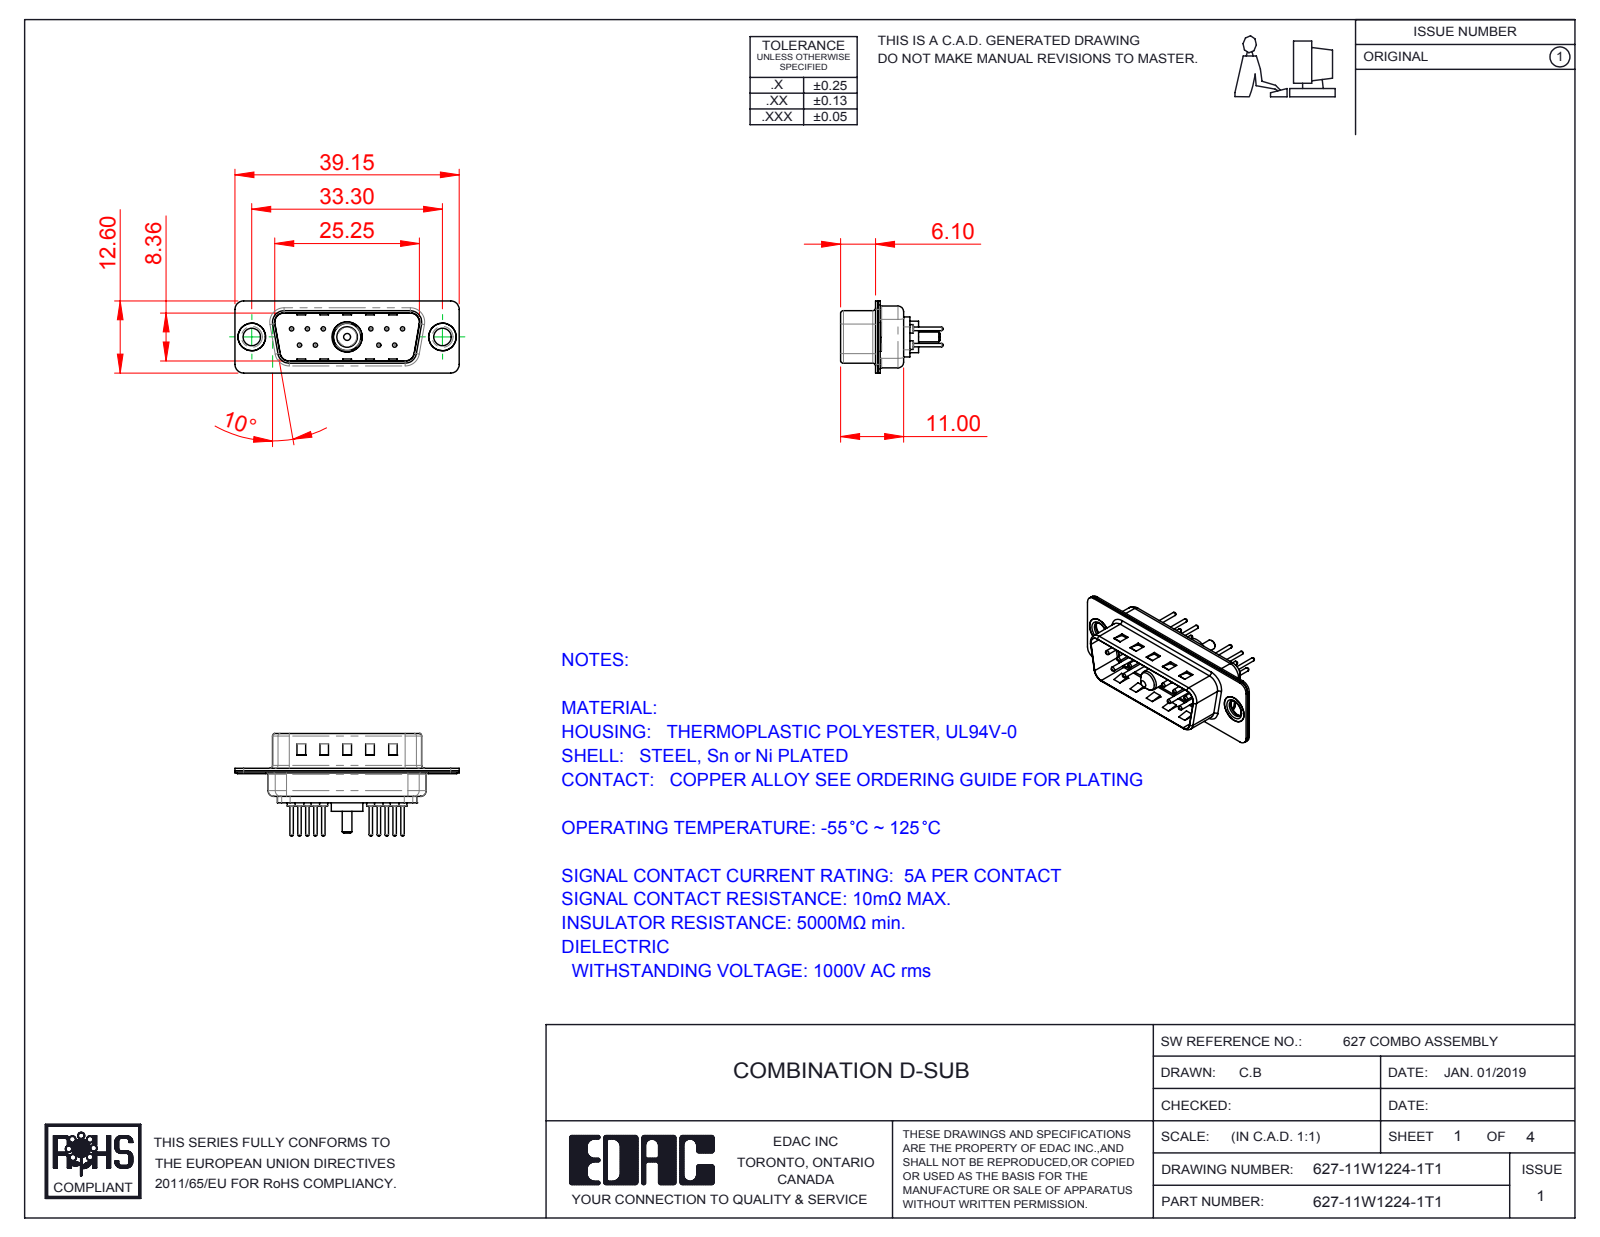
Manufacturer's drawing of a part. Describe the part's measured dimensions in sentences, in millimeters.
The part is named "627Combo Housing_11W1; 627Combo Shell Rear_15 Contacts; 627Combo Shell Front_15 Contacts; 627Combo Thru Hole Rivet (+4 more)". Its 3-D file was written by "SolidWorks 2016 (CONFIG_CONTROL_DESIGN)". It is 17 solids with 737 faces: 228 planar, 280 cylindrical and 229 other. Overall it measures 39.15 by 17.9 by 12.6 millimeters. Its volume is 1 819 cubic millimeters and its surface area 4 631 square millimeters. Round holes: 10 of diameter 0.75, 10 of diameter 1.6, 10 of diameter 2, 2 of diameter 3.05, 2 of diameter 4, 2 of diameter 4.8, 1 of diameter 4.85, 1 of diameter 5.3. Round bosses or shafts: 10 of diameter 1.5, 10 of diameter 0.6, 2 of diameter 5, 2 of diameter 4.9, 2 of diameter 3.55, 1 of diameter 5.5, 1 of diameter 5.2, 1 of diameter 4.75. Partial cylindrical surfaces (rounded edges, fillets, slot ends): 20 of radius 1.5, 12 of radius 2, 8 of radius 0.5, 8 of radius 1.6, 7 of radius 1, 4 of radius 0.25, 4 of radius 0.6, 4 of radius 0.65. The main face-to-face distances are 0.4, 0.82, 9.58, 0.8, 8.76, 1.5, 5.6, 5.2, 6, 1.22. The hole center spacings are 3.16, 2.77, 13.85, 11.08, 16.62, 5.03, 5.04, 5.54.
